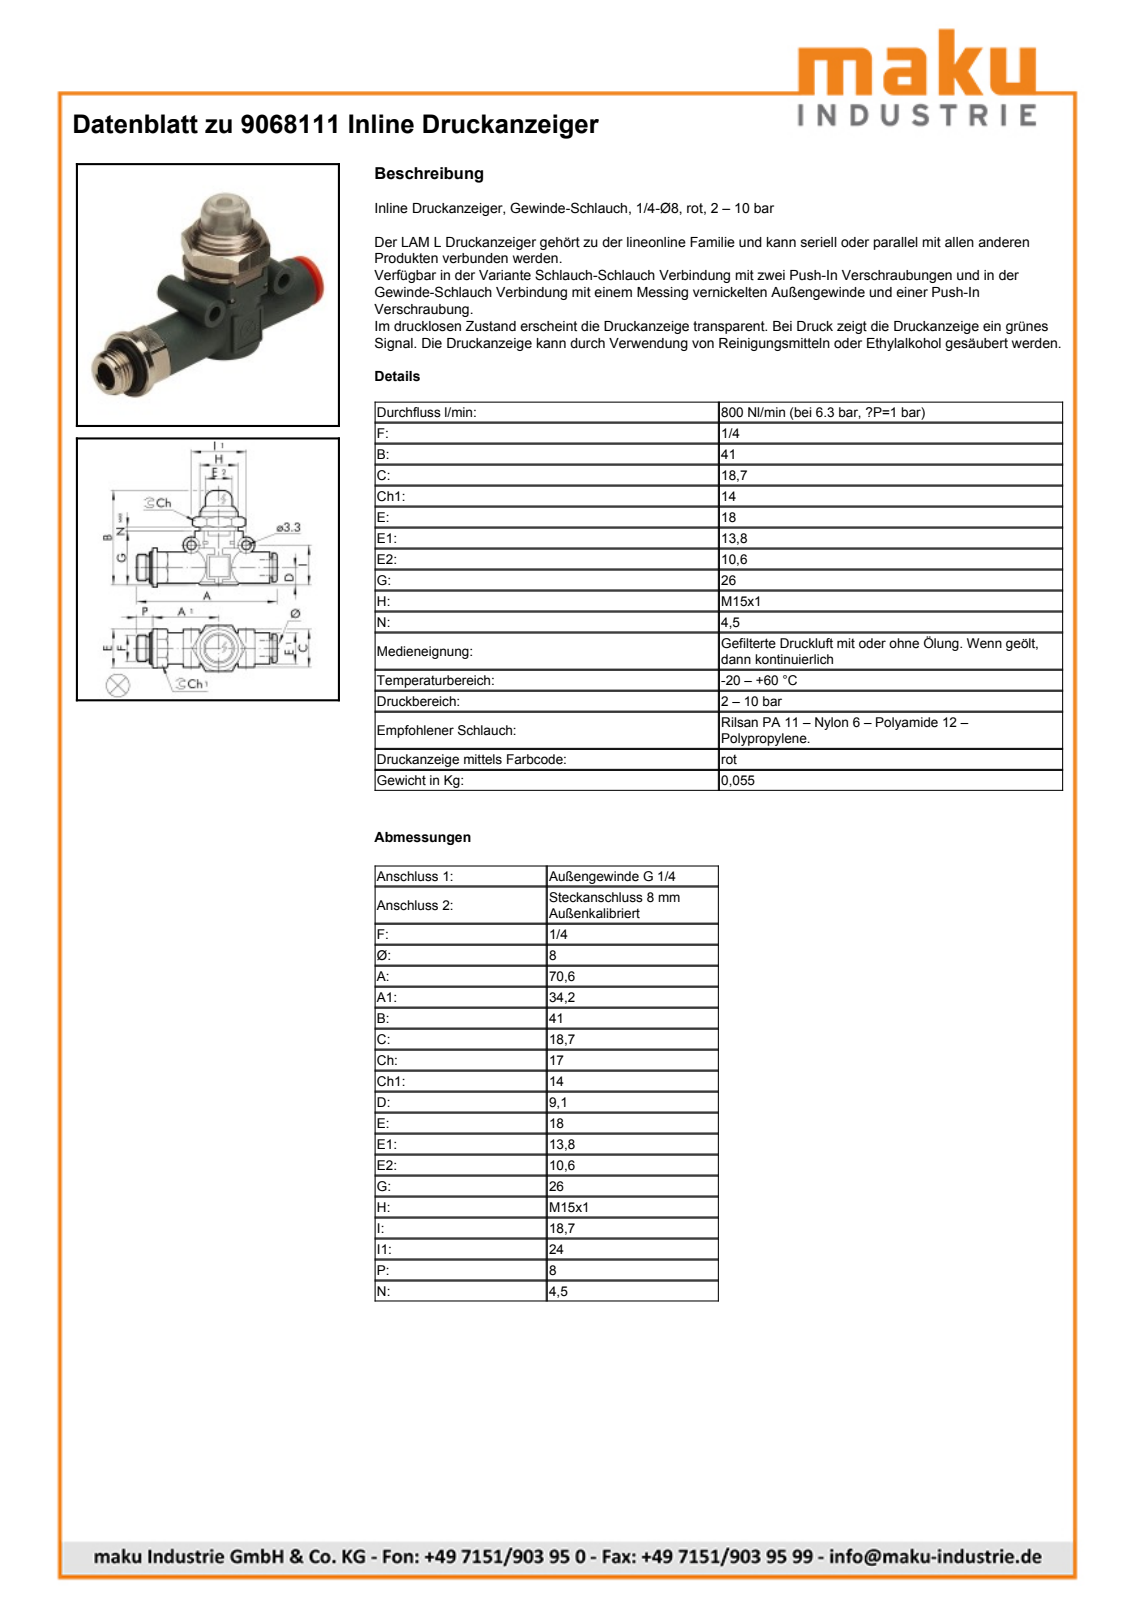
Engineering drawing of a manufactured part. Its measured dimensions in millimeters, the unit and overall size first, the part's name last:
Units: millimetres
Overall size (bounding box): 70.6 × 41 × 18.7
Round holes (diameter × count): ⌀3.3 ×2, ⌀6 ×2, ⌀5.5 ×1, ⌀8 ×1, ⌀8.1 ×1, ⌀11 ×1, ⌀11.65 ×1, ⌀12.5 ×1, ⌀15 ×1
Round bosses / shafts (diameter × count): ⌀6 ×2, ⌀18.8 ×1, ⌀18 ×1, ⌀14 ×1, ⌀13.8 ×1, ⌀13.6 ×1, ⌀13.16 ×1, ⌀11.1 ×1
Partial cylindrical surfaces — rounded edges, fillets, slot ends (radius × count): R3.75 ×1, R7.95 ×1, R9.65 ×1, R10.2 ×1, R10.35 ×1, R11.45 ×1
Main face-to-face distances: 24.1, 1.9, 4.1, 20, 2, 26, 21.9, 18.5, 11.2, 20.5
Hole centre spacings: 15.37, 24
Volume: 11 880 mm³ · Surface area: 10 623 mm²
Bodies: 4 solids, 178 faces (94 planar, 58 cylindrical, 26 other)
Part name (STEP PRODUCT): 9068111; LINE-ON-LINE D8 V2v/V3V_L body; LINE-ON-LINE D8 VNR-L bushing; LINE-ON-LINE D8-1/4 thread port (+1 more)
STEP written by: PARTsolutions (AUTOMOTIVE_DESIGN)
